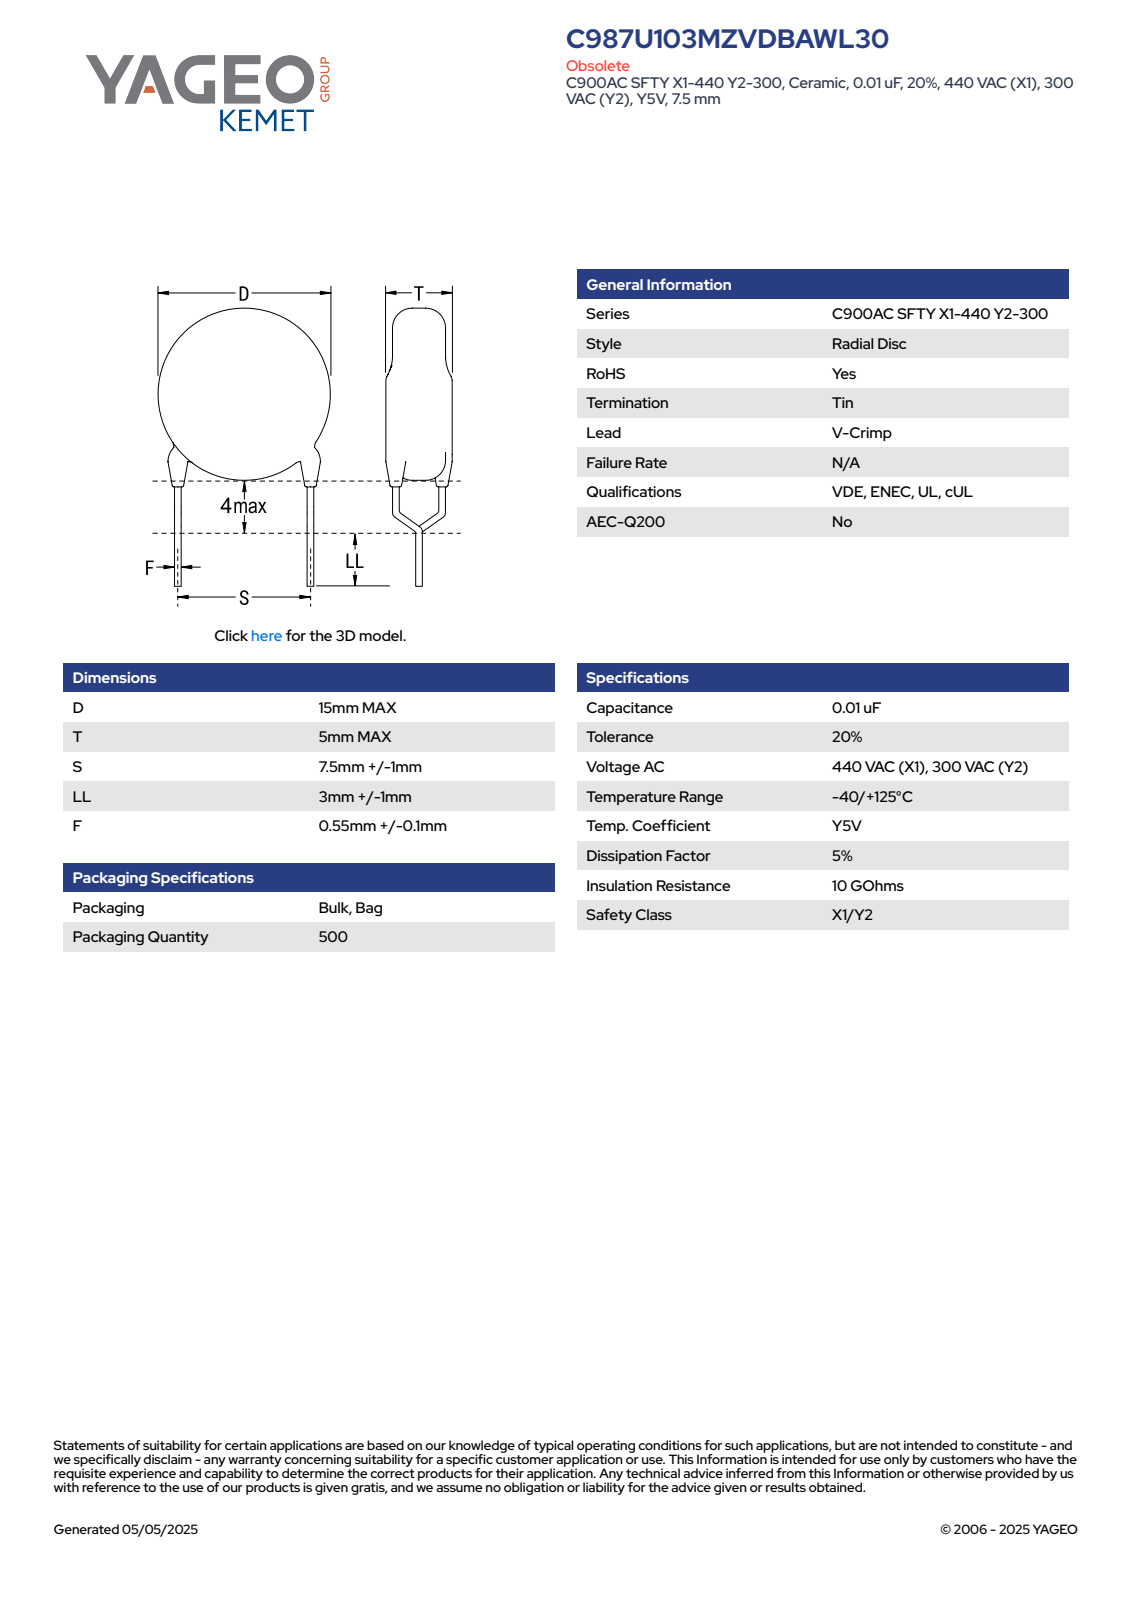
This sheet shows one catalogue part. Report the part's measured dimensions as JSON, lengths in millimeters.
{"part_name": "CCD_VCC900_D15T5S7.5LL4F0.65", "step_written_by": "SolidWorks 2014 (AUTOMOTIVE_DESIGN)", "units": "millimeters", "bodies": {"solids": 5, "faces": 93, "planar": 65, "cylindrical": 16, "other": 12}, "overall_size": [22.8, 15, 5], "volume_mm3": 871, "surface_area_mm2": 610, "round_bosses_or_shafts": [[0.65, 6], [15, 1]], "face_to_face_distances": [5, 6.9, 16.27, 9.37, 14.32, 7.42, 1.95, 0.53, 7.96, 0.37]}
